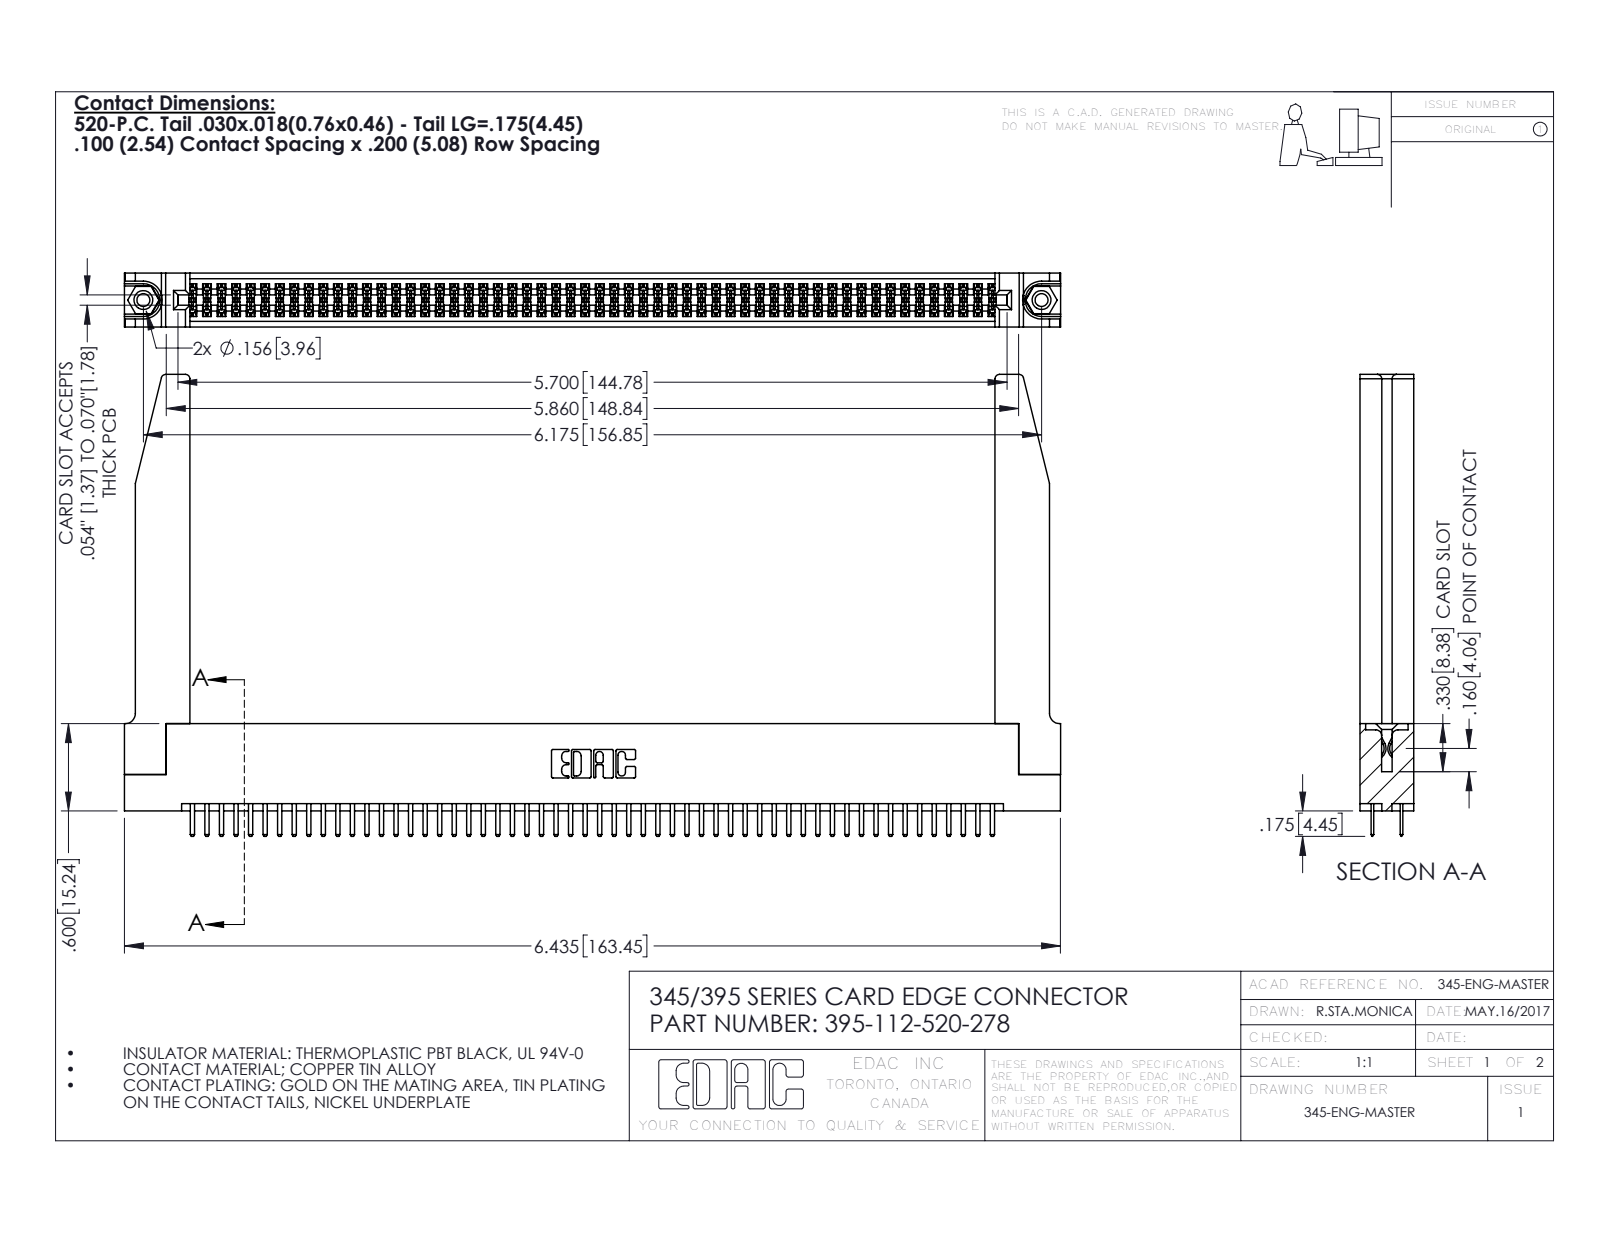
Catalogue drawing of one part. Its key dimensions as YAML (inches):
part_name: "345-292-001_345-293-120; 345-250-001_345-250-001-102; 345-220-078_345-220-078; 345 Part_Flush Mounting Lugs - 0.156 Dia-TH (+1 more)"
step_written_by: "SolidWorks 2016 (CONFIG_CONTROL_DESIGN)"
units: inches
bodies: {solids: 117, faces: 6408, planar: 4142, cylindrical: 2214, other: 52}
overall_size: [6.436, 3.175, 0.37]
volume: 1.448
surface_area: 47.43
round_holes:
  - {diameter: 0.089, count: 2}
  - {diameter: 0.125, count: 2}
  - {diameter: 0.156, count: 2}
  - {diameter: 0.064, count: 1}
round_bosses_or_shafts:
  - {diameter: 0.155, count: 2}
partial_cylinders:
  - {radius: 0.006, count: 168}
  - {radius: 0.01, count: 116}
  - {radius: 0.01, count: 22}
  - {radius: 0.03, count: 8}
  - {radius: 0.007, count: 6}
  - {radius: 0.031, count: 6}
  - {radius: 0.026, count: 3}
  - {radius: 0.014, count: 2}
face_to_face_distances: [0.072, 0.37, 0.298, 0.2, 0.098, 0.272, 0.025, 0.225, 0.022, 0.072]
hole_center_spacings: [0.27, 5.939, 6.175]
